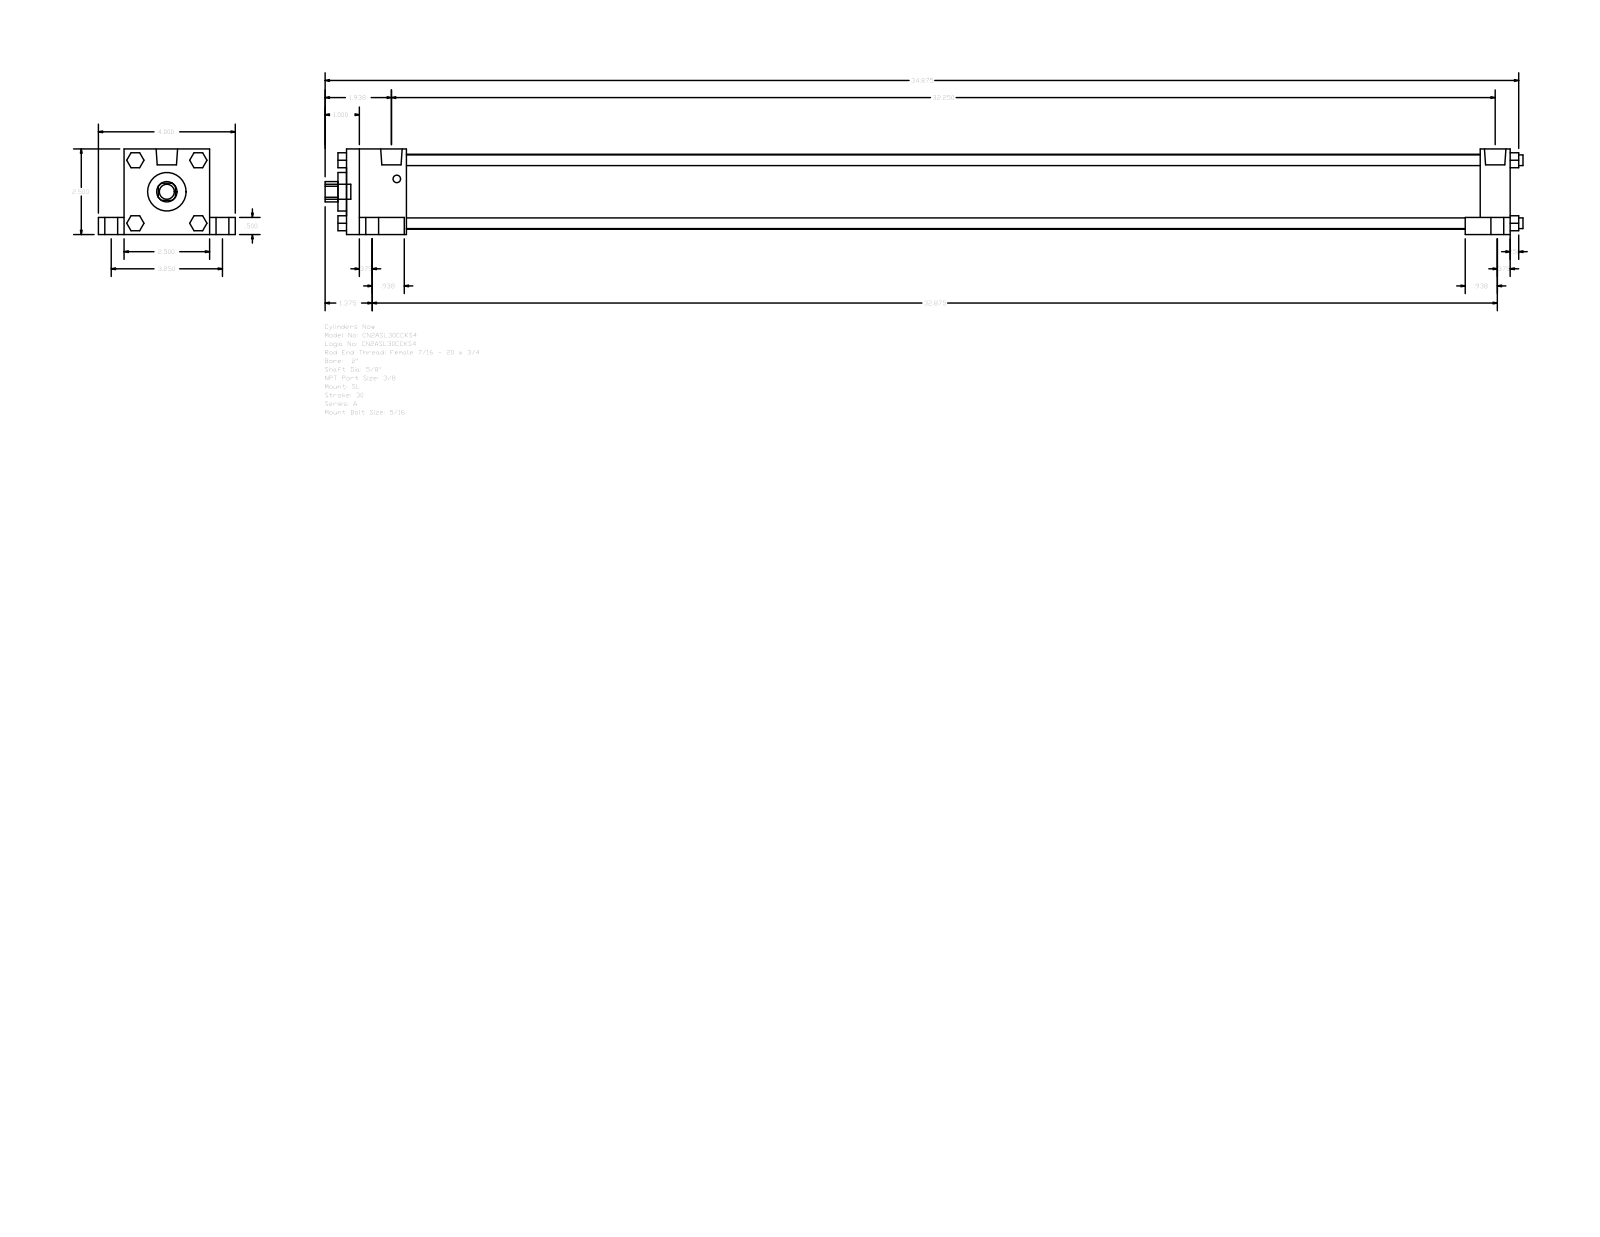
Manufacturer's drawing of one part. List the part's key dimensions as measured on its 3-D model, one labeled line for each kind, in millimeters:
Part name (STEP PRODUCT): A_SL__0200_0.625
STEP written by: GSSL Pune (CONFIG_CONTROL_DESIGN)
Units: millimetres
Bodies: 0 solids, 148 faces (112 planar, 36 cylindrical, 0 other)
Overall size (bounding box): 889 × 101.6 × 63.5
Round holes (diameter × count): ⌀15.88 ×1, ⌀28.57 ×1, ⌀55.63 ×1
Round bosses / shafts (diameter × count): ⌀15.88 ×4, ⌀9.53 ×4, ⌀7.94 ×4, ⌀5.56 ×4, ⌀15.93 ×2, ⌀11.11 ×1
Partial cylindrical surfaces — rounded edges, fillets, slot ends (radius × count): R7.54 ×1
Main face-to-face distances: 63.5, 863.6, 50.8, 12.7, 19.05, 82.55, 44.45, 819.15, 841.37, 796.92
